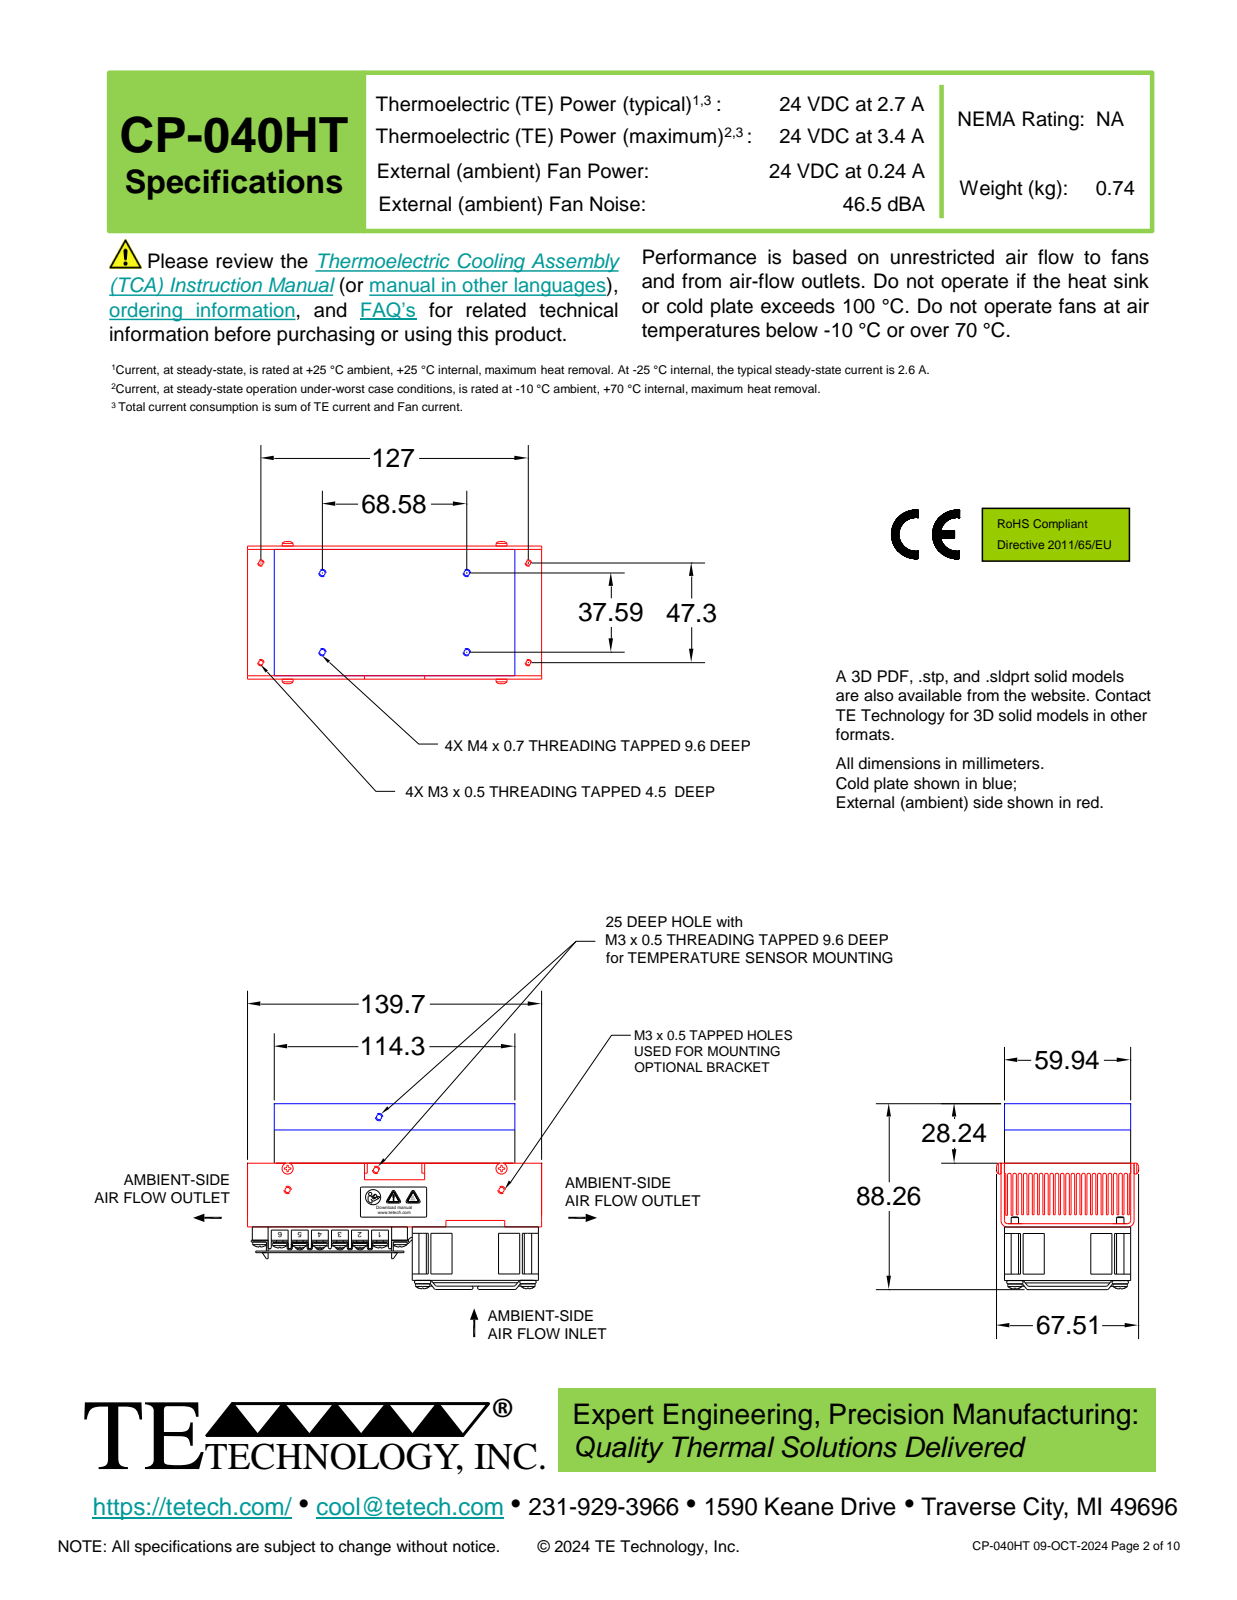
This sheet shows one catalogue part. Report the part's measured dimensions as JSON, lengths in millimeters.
{"part_name": "cold plate CP-040HT; heat sink CP-040HT; thermal pad CP-040HT; dummy 30x34x3.6 PORCH (+8 more)", "step_written_by": "Alibre (AUTOMOTIVE_DESIGN)", "units": "millimeters", "bodies": {"solids": 129, "faces": 2937, "planar": 1585, "cylindrical": 591, "other": 761}, "overall_size": [139.7, 88.6, 66.6], "volume_mm3": 339200, "surface_area_mm2": 277000, "round_holes": [[2.6, 25], [1.9, 4], [2.5, 4], [3.3, 4], [3.5, 4], [3.9, 4], [4.3, 4], [4.5, 4], [4.7, 4], [4.2, 3], [4.2, 3], [4.3, 3]], "round_bosses_or_shafts": [[3.5, 23], [6.9, 20], [1.4, 14], [1.8, 12], [1.6, 11], [9.5, 4], [4.9, 4], [3.5, 4]], "partial_cylinders_radius": [[0.3, 39], [1, 36], [0.7, 25], [1, 21], [0.8, 16], [0.3, 11], [0.4, 8], [0.8, 8]], "face_to_face_distances": [2.5, 5, 7.4, 9.9, 12.4, 34.7, 14.9, 37.2, 32.2, 17.3], "hole_center_spacings": [7.9, 19.1, 20.6, 50, 9.5, 12.3, 20.4, 29.6]}
